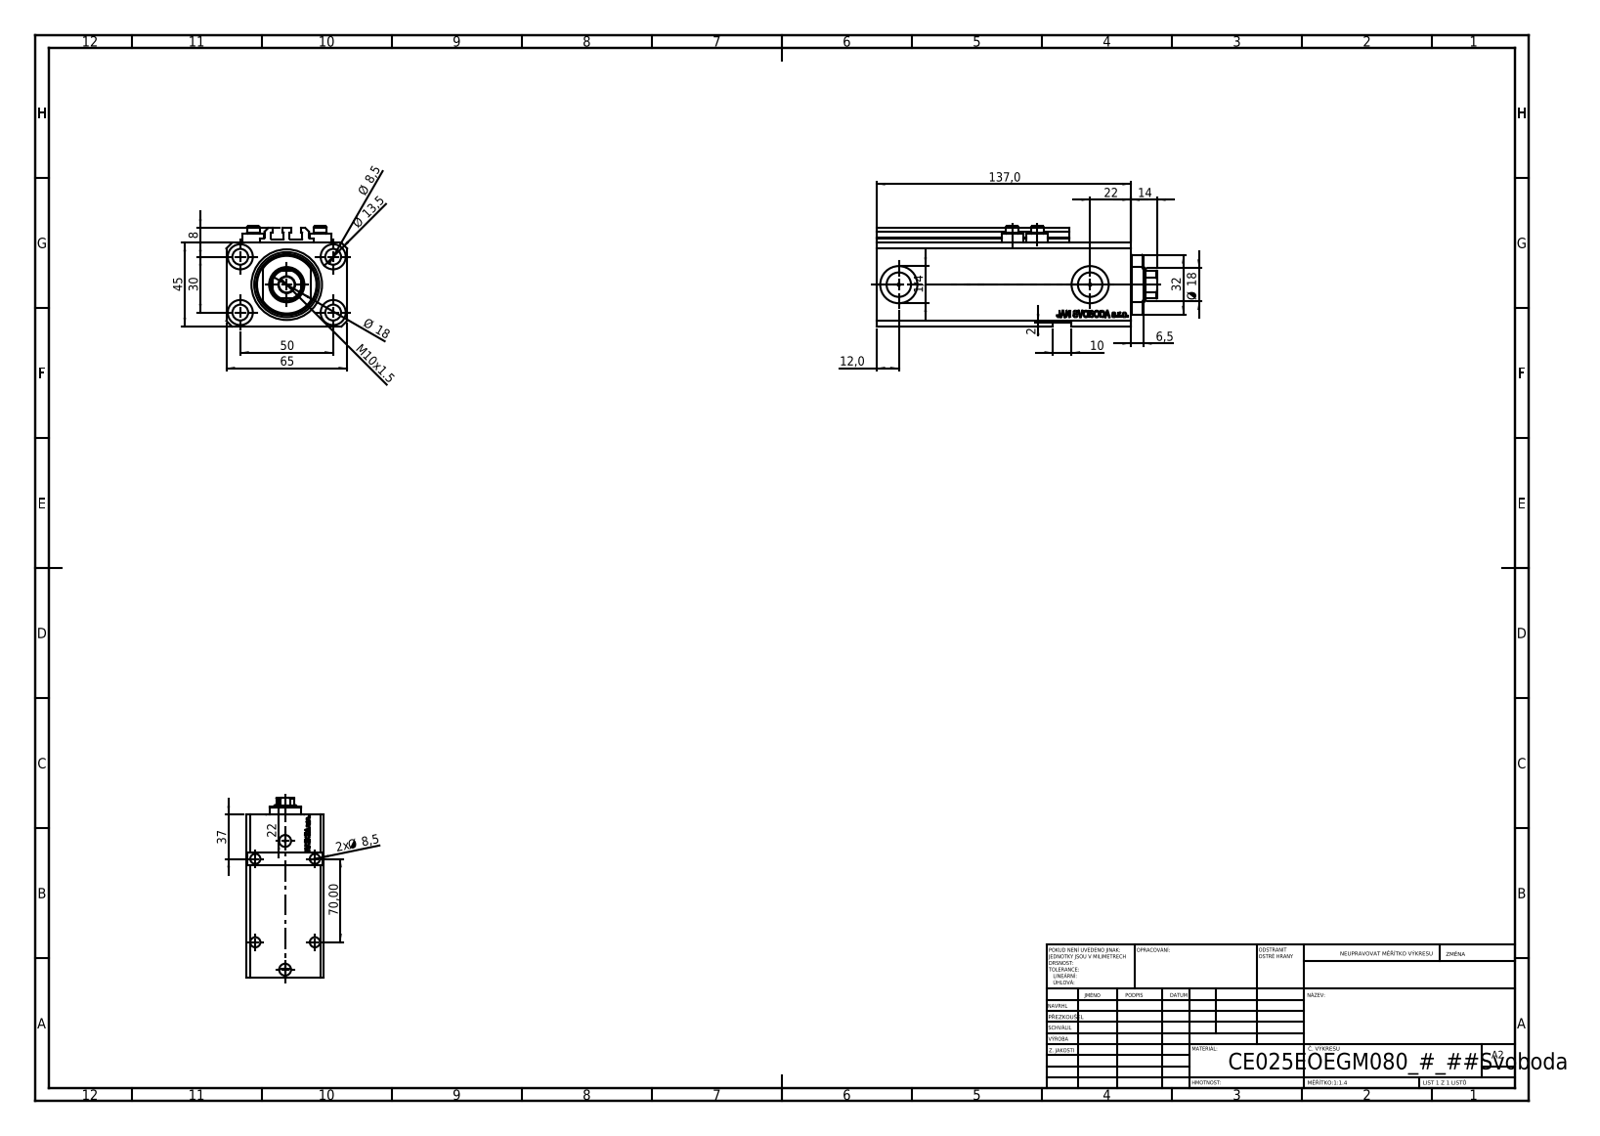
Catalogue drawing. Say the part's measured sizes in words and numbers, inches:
The part is named "ALLEN BOLT V250CE; V250CE_C_VCP; V250CE_VC_E; V250CE_E_Body". Its 3-D file was written by "SolidWorks 2019 (CONFIG_CONTROL_DESIGN)". It is 8 solids with 1087 faces: 511 planar, 146 cylindrical and 430 other. Overall it measures 5.945 by 2.559 by 2.126 inches. Its volume is 21.39 cubic inches and its surface area 145 square inches. Round holes: 9 of diameter 0.335, 4 of diameter 0.049, 4 of diameter 0.157, 4 of diameter 0.531, 2 of diameter 0.394, 2 of diameter 0.518, 2 of diameter 0.787, 1 of diameter 0.709, 1 of diameter 0.984, 1 of diameter 1.496. Round bosses or shafts: 4 of diameter 0.457, 4 of diameter 0.276. Partial cylindrical surfaces (rounded edges, fillets, slot ends): 10 of radius 0.008, 1 of radius 0.335, 1 of radius 0.63. The main face-to-face distances are 1.772, 2.559, 1.85, 0.079, 4.843, 0.098, 0.551, 0.394, 5.394, 0.807. The hole center spacings are 1.148, 1.969, 0.535, 0.595, 1.098, 1.181, 1.323, 1.324.
